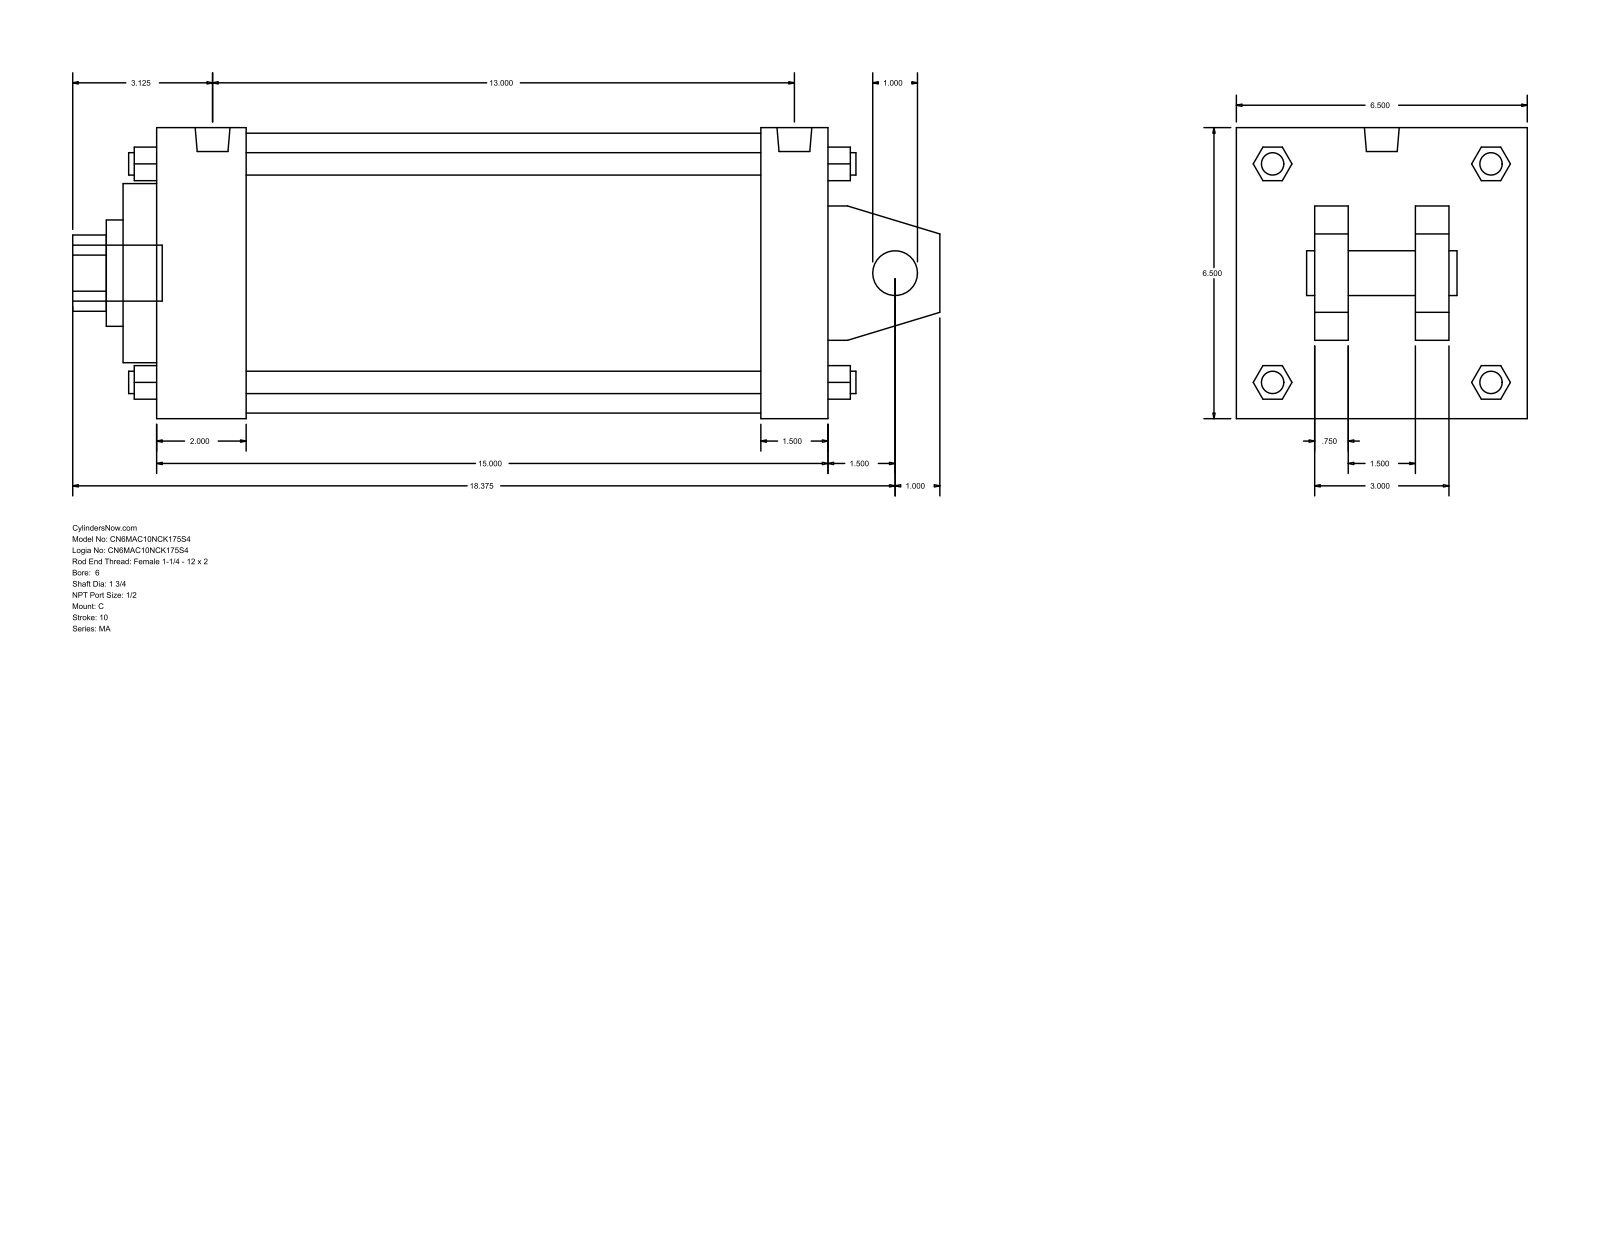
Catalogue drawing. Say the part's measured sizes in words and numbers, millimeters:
The part is named "MA_C__0600_1.75". Its 3-D file was written by "GSSL Pune (CONFIG_CONTROL_DESIGN)". It is 0 solids with 141 faces: 109 planar, 32 cylindrical and 0 other. Overall it measures 492.12 by 165.1 by 165.1 millimeters. Round holes: 1 of diameter 25.4, 1 of diameter 44.45, 1 of diameter 60.33, 1 of diameter 101.6, 1 of diameter 158.75. Round bosses or shafts: 4 of diameter 17.46, 4 of diameter 12.7, 2 of diameter 19.77, 1 of diameter 31.75. Partial cylindrical surfaces (rounded edges, fillets, slot ends): 1 of radius 21.63. The main face-to-face distances are 165.1, 381, 19.05, 38.1, 63.5, 101.6, 50.8, 120.65, 44.45, 342.9.
